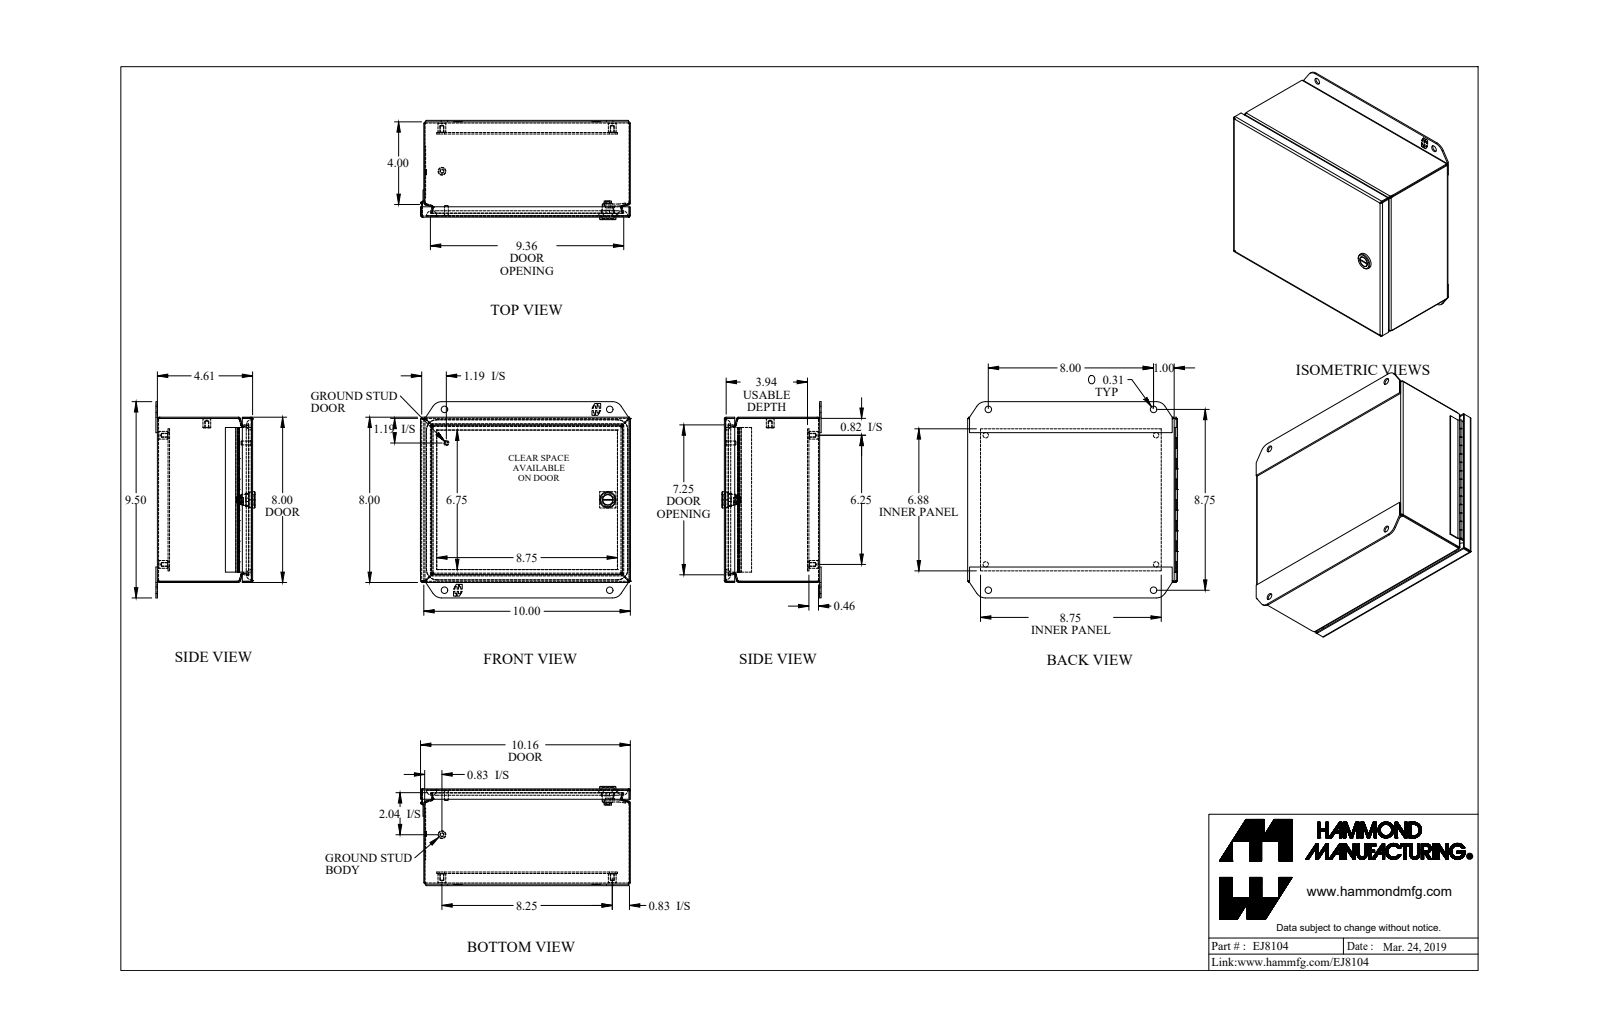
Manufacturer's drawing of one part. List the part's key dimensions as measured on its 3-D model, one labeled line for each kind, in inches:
Part name (STEP PRODUCT): EJ8104_Default
STEP written by: SolidWorks 2019 (CONFIG_CONTROL_DESIGN)
Units: inches
Bodies: 16 solids, 643 faces (361 planar, 190 cylindrical, 92 other)
Overall size (bounding box): 10.165 × 9.5 × 4.805
Volume: 29.71 in³ · Surface area: 972.5 in²
Round holes (diameter × count): ⌀0.156 ×5, ⌀0.265 ×4, ⌀0.313 ×4, ⌀0.05 ×1, ⌀0.516 ×1
Round bosses / shafts (diameter × count): ⌀0.375 ×5, ⌀0.788 ×1, ⌀0.535 ×1, ⌀0.496 ×1, ⌀0.435 ×1, ⌀0.25 ×1, ⌀0.188 ×1, ⌀0.1 ×1
Partial cylindrical surfaces — rounded edges, fillets, slot ends (radius × count): R0.029 ×16, R0.086 ×16, R0.281 ×10, R0.25 ×4, R0.499 ×4, R0.5 ×4, R0.06 ×2, R0.539 ×2
Main face-to-face distances: 0.057, 4.554, 0.072, 0.589, 7.943, 4.611, 4.497, 9.943, 0.46, 0.517
Hole centre spacings: 1.256, 7.502, 8.22, 10.35, 11.057, 6.25, 6.25, 8.25
